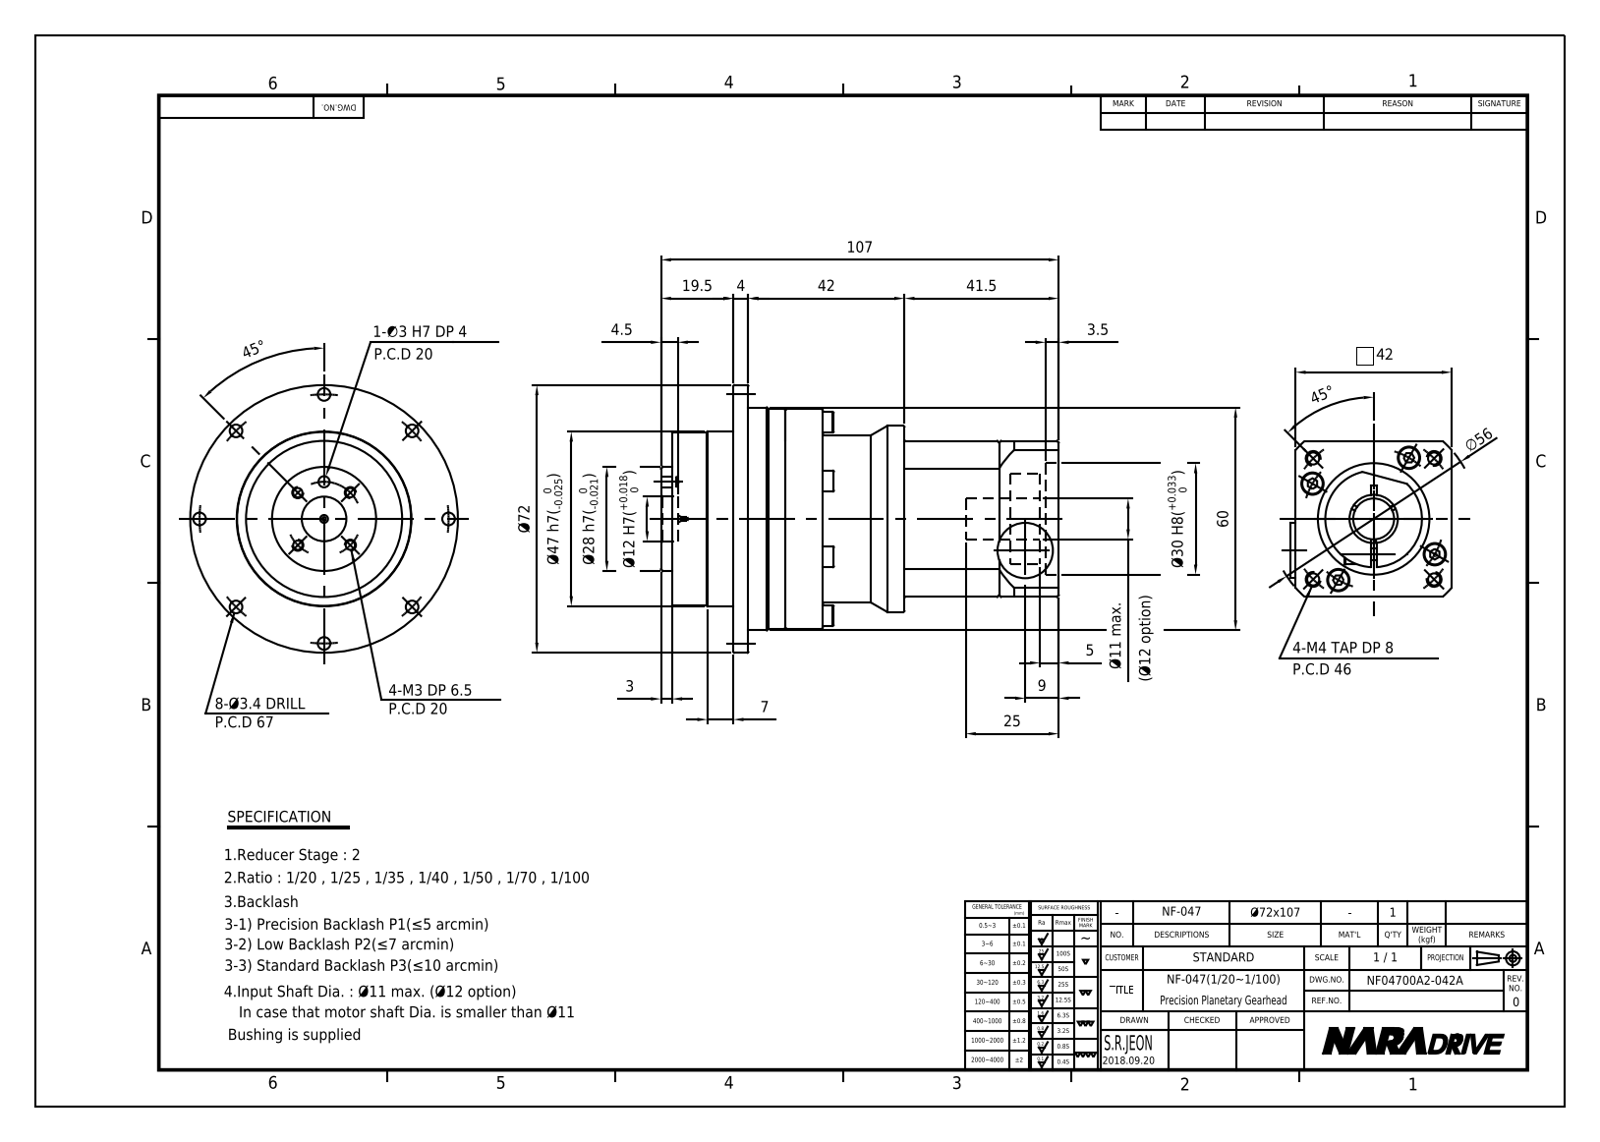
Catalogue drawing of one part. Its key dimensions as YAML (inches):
part_name: "NF04700A2-042A"
step_written_by: "Autodesk Inventor 2015 (AUTOMOTIVE_DESIGN)"
units: inches
bodies: {solids: 2, faces: 455, planar: 209, cylindrical: 122, other: 124}
overall_size: [4.213, 2.835, 2.835]
volume: 8.351
surface_area: 77.87
round_holes:
  - {diameter: 0.134, count: 25}
  - {diameter: 0.097, count: 17}
  - {diameter: 0.236, count: 8}
  - {diameter: 0.128, count: 4}
  - {diameter: 0.039, count: 1}
  - {diameter: 0.118, count: 1}
  - {diameter: 0.276, count: 1}
  - {diameter: 0.335, count: 1}
  - {diameter: 0.433, count: 1}
  - {diameter: 0.472, count: 1}
  - {diameter: 0.512, count: 1}
  - {diameter: 1.063, count: 1}
round_bosses_or_shafts:
  - {diameter: 0.217, count: 13}
  - {diameter: 0.118, count: 13}
  - {diameter: 2.835, count: 1}
  - {diameter: 2.362, count: 1}
  - {diameter: 2.323, count: 1}
  - {diameter: 1.969, count: 1}
  - {diameter: 1.85, count: 1}
  - {diameter: 1.831, count: 1}
partial_cylinders:
  - {radius: 0.118, count: 1}
  - {radius: 1.102, count: 1}
face_to_face_distances: [1.654, 1.201, 0.472, 0.256, 1.969, 0.807, 0.157, 1.043, 0.65, 1.673]
hole_center_spacings: [1.6, 1.319, 1.009, 1.367, 1.669, 0.937, 1.416, 1.418]
